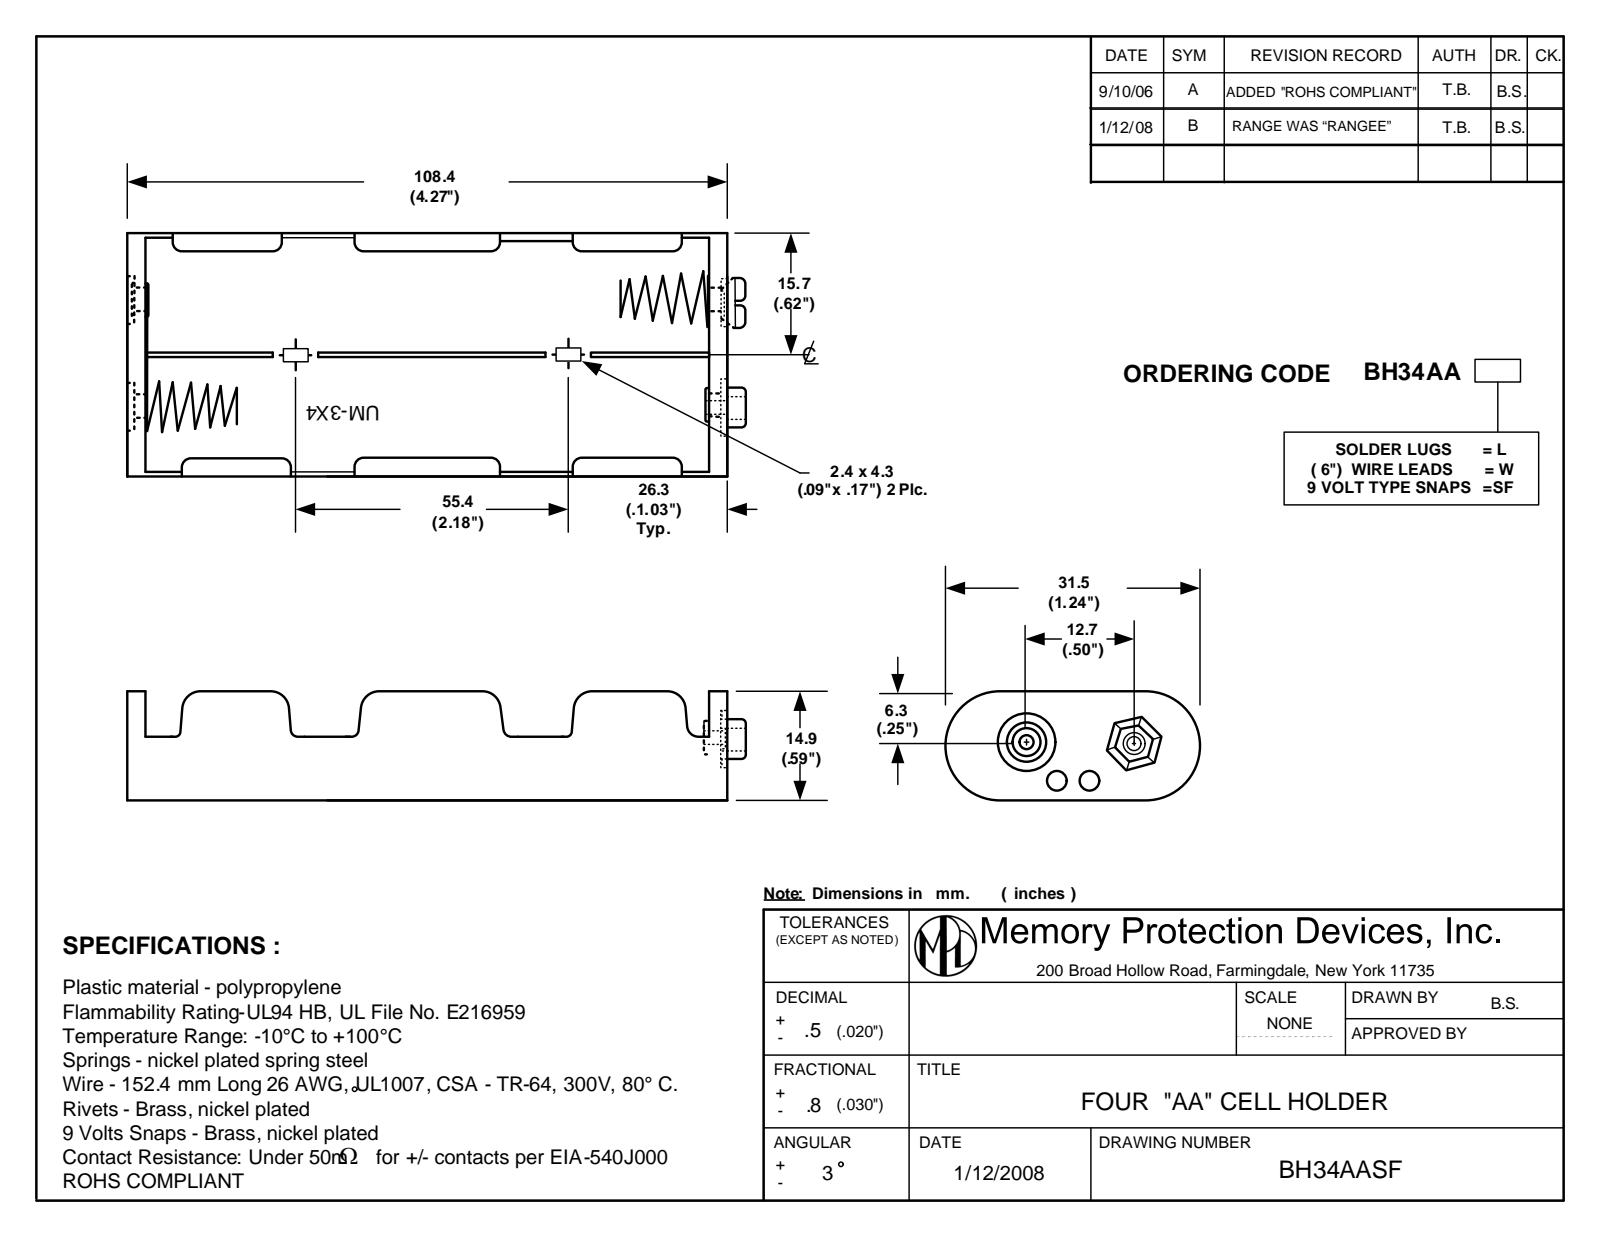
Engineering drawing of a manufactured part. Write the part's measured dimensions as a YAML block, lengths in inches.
part_name: "BH34AASF"
step_written_by: "SolidWorks 2017 (AUTOMOTIVE_DESIGN)"
units: inches
bodies: {solids: 5, faces: 326, planar: 158, cylindrical: 113, other: 55}
overall_size: [4.413, 1.24, 0.587]
volume: 0.475
surface_area: 22.58
round_holes:
  - {diameter: 0.055, count: 4}
  - {diameter: 0.087, count: 2}
  - {diameter: 0.315, count: 2}
  - {diameter: 0.368, count: 2}
  - {diameter: 0.195, count: 1}
round_bosses_or_shafts:
  - {diameter: 0.138, count: 2}
  - {diameter: 0.134, count: 2}
  - {diameter: 0.028, count: 2}
  - {diameter: 0.225, count: 1}
partial_cylinders:
  - {radius: 0.039, count: 18}
  - {radius: 0.016, count: 12}
  - {radius: 0.035, count: 6}
  - {radius: 0.228, count: 4}
  - {radius: 0.276, count: 4}
face_to_face_distances: [0.047, 0.039, 4.22, 4.173, 4.268, 0.012, 4.256, 0.035, 4.208, 1.193]
hole_center_spacings: [0.102, 0.324, 0.326, 0.406, 0.409, 0.591, 3.39]
